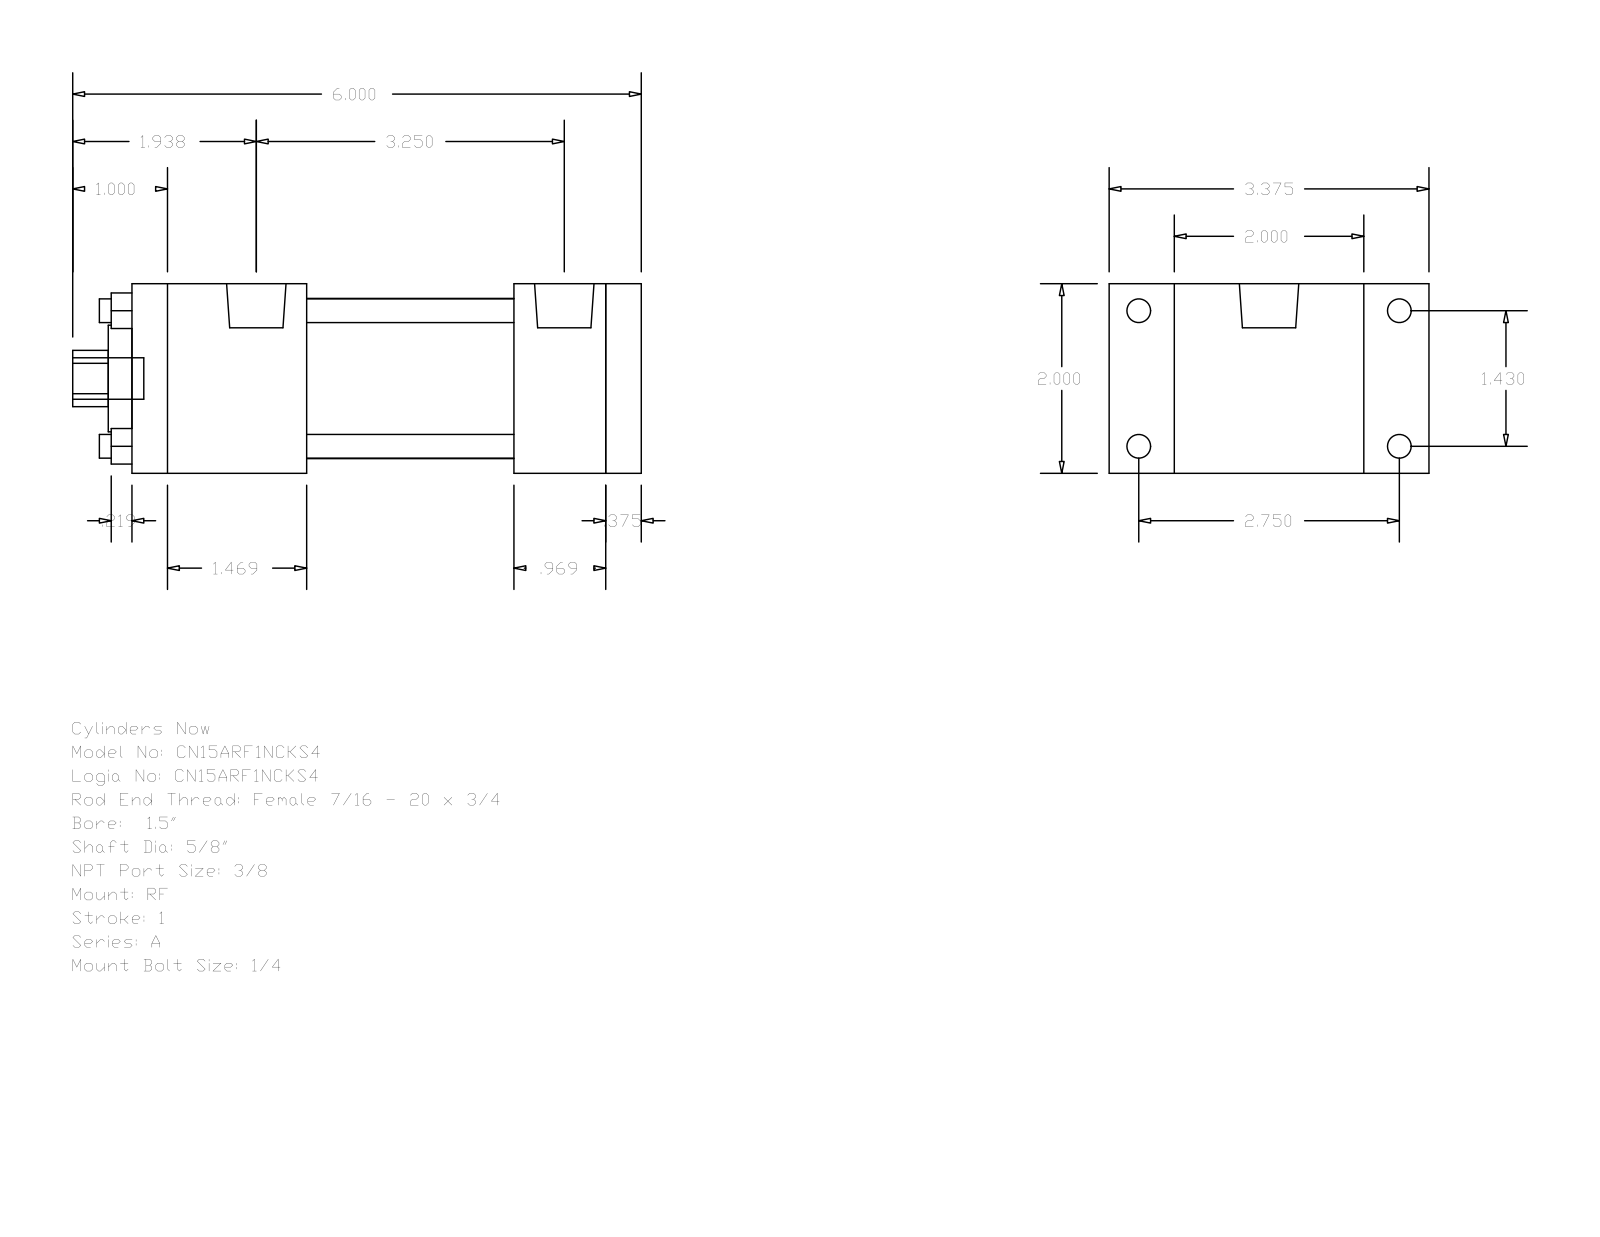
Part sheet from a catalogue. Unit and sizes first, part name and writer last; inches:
Units: inches
Overall size (bounding box): 6 × 3.375 × 2
Round holes (diameter × count): ⌀0.25 ×4, ⌀0.625 ×1, ⌀1.125 ×1, ⌀1.69 ×1
Round bosses / shafts (diameter × count): ⌀0.25 ×4, ⌀0.219 ×4, ⌀0.627 ×2, ⌀0.437 ×1
Partial cylindrical surfaces — rounded edges, fillets, slot ends (radius × count): R0.297 ×1
Main face-to-face distances: 2, 0.375, 5, 5.375, 4.031, 0.969, 1.344, 1.844, 2.187, 3.156
Hole centre spacings: 1.011, 1.43, 2.022
Bodies: 0 solids, 92 faces (64 planar, 28 cylindrical, 0 other)
Part name (STEP PRODUCT): A_RF__0150_0.625
STEP written by: GSSL Pune (CONFIG_CONTROL_DESIGN)
